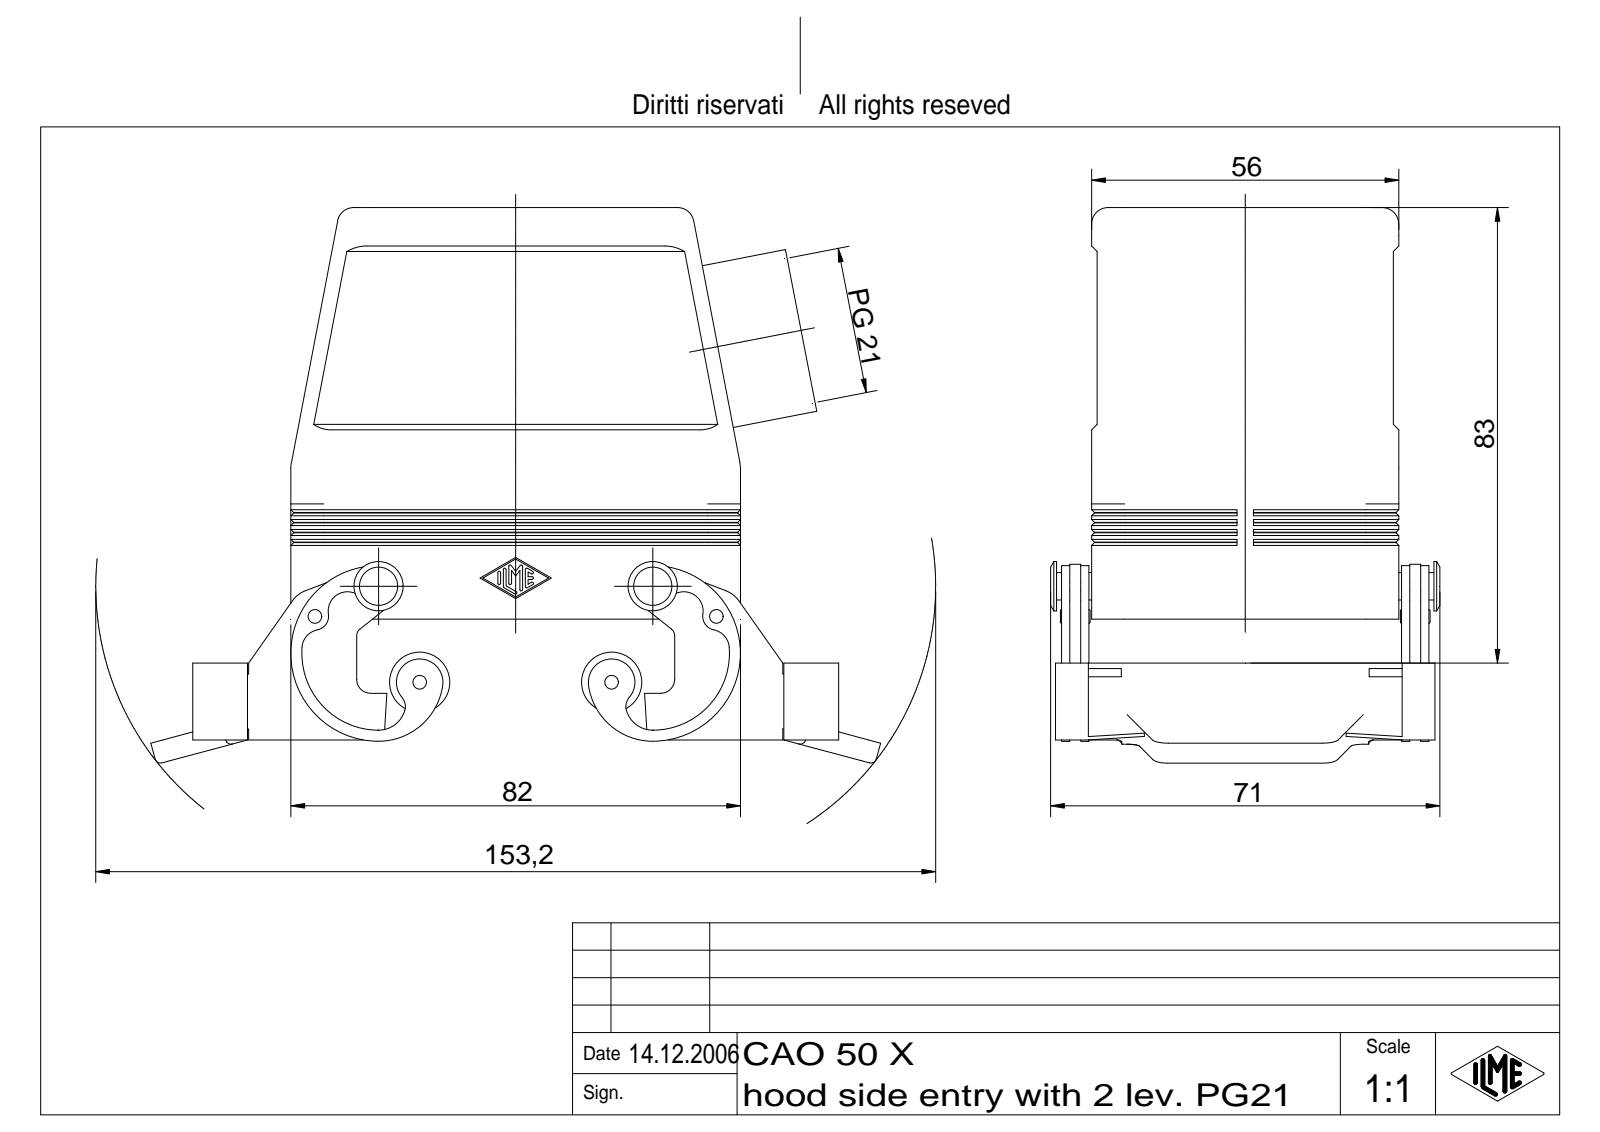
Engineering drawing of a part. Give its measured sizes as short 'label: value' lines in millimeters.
name: CAO 50 X
written by: Autodesk Inventor 7 (AUTOMOTIVE_DESIGN)
unit: mm
bodies: 1 solid, 889 faces (261 planar, 258 cylindrical, 370 other)
size: 133.07 × 101.22 × 71
volume: 100 422 mm³; area: 66 540 mm²
holes: 4× ⌀2.46, 4× ⌀3.5, 2× ⌀2.5, 1× ⌀24.78, 1× ⌀26.78
bosses: 2× ⌀11, 2× ⌀9, 2× ⌀5, 2× ⌀2, 1× ⌀30
rounds: 14× R0.25, 14× R2, 12× R3, 10× R6, 8× R1, 6× R2.5, 4× R3.5, 4× R5
face distances: 3, 53, 50, 2, 55, 56, 1, 52, 11.25, 70.75
hole spacings: 16, 66, 67.91, 73.2
